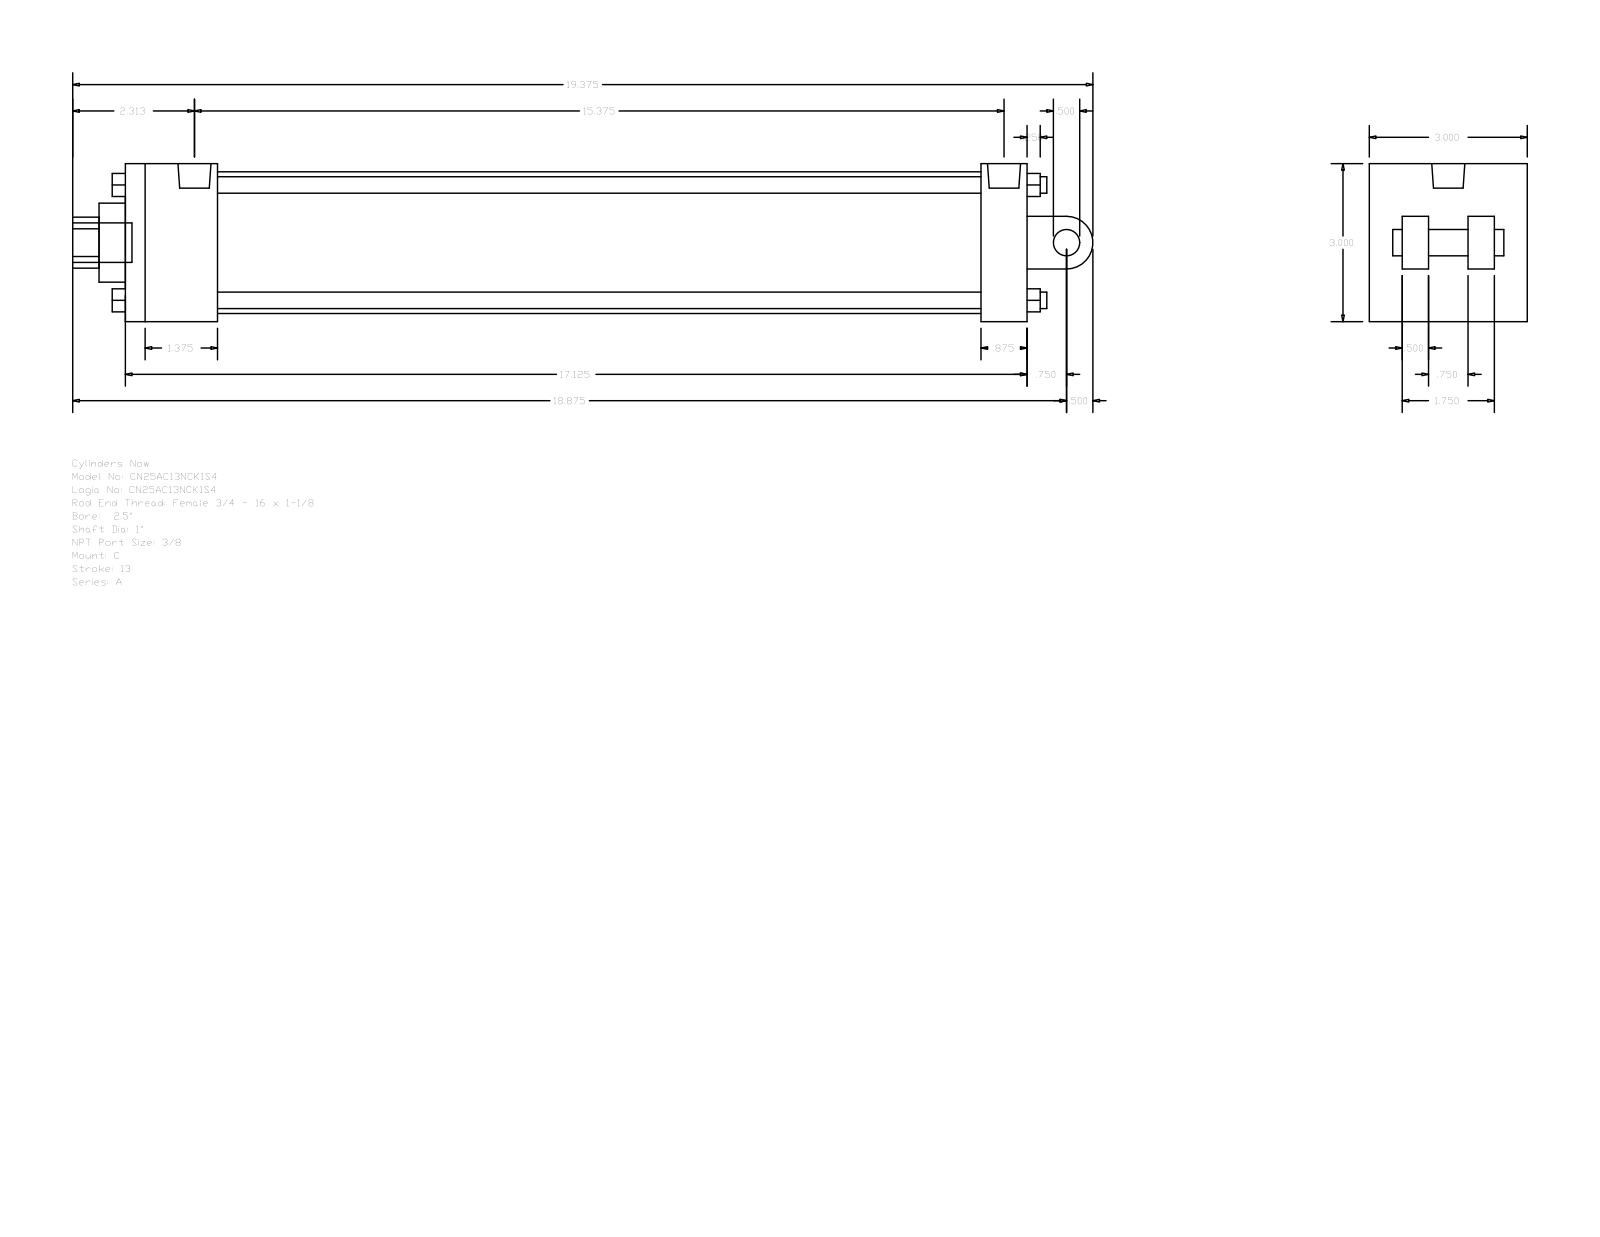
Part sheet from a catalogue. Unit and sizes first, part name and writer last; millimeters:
Units: millimetres
Overall size (bounding box): 492.12 × 76.2 × 76.2
Round holes (diameter × count): ⌀5.56 ×2, ⌀15.93 ×1, ⌀25.4 ×1, ⌀38.1 ×1, ⌀68.33 ×1
Round bosses / shafts (diameter × count): ⌀7.94 ×4, ⌀5.56 ×2, ⌀19.05 ×1, ⌀15.93 ×1, ⌀12.7 ×1
Partial cylindrical surfaces — rounded edges, fillets, slot ends (radius × count): R12.29 ×1, R12.7 ×1
Main face-to-face distances: 76.2, 434.98, 12.7, 44.45, 412.75, 368.3, 390.53, 22.23, 15.87, 25.4
Hole centre spacings: 2.38
Bodies: 0 solids, 135 faces (102 planar, 33 cylindrical, 0 other)
Part name (STEP PRODUCT): A_C__0250_1
STEP written by: GSSL Pune (CONFIG_CONTROL_DESIGN)
